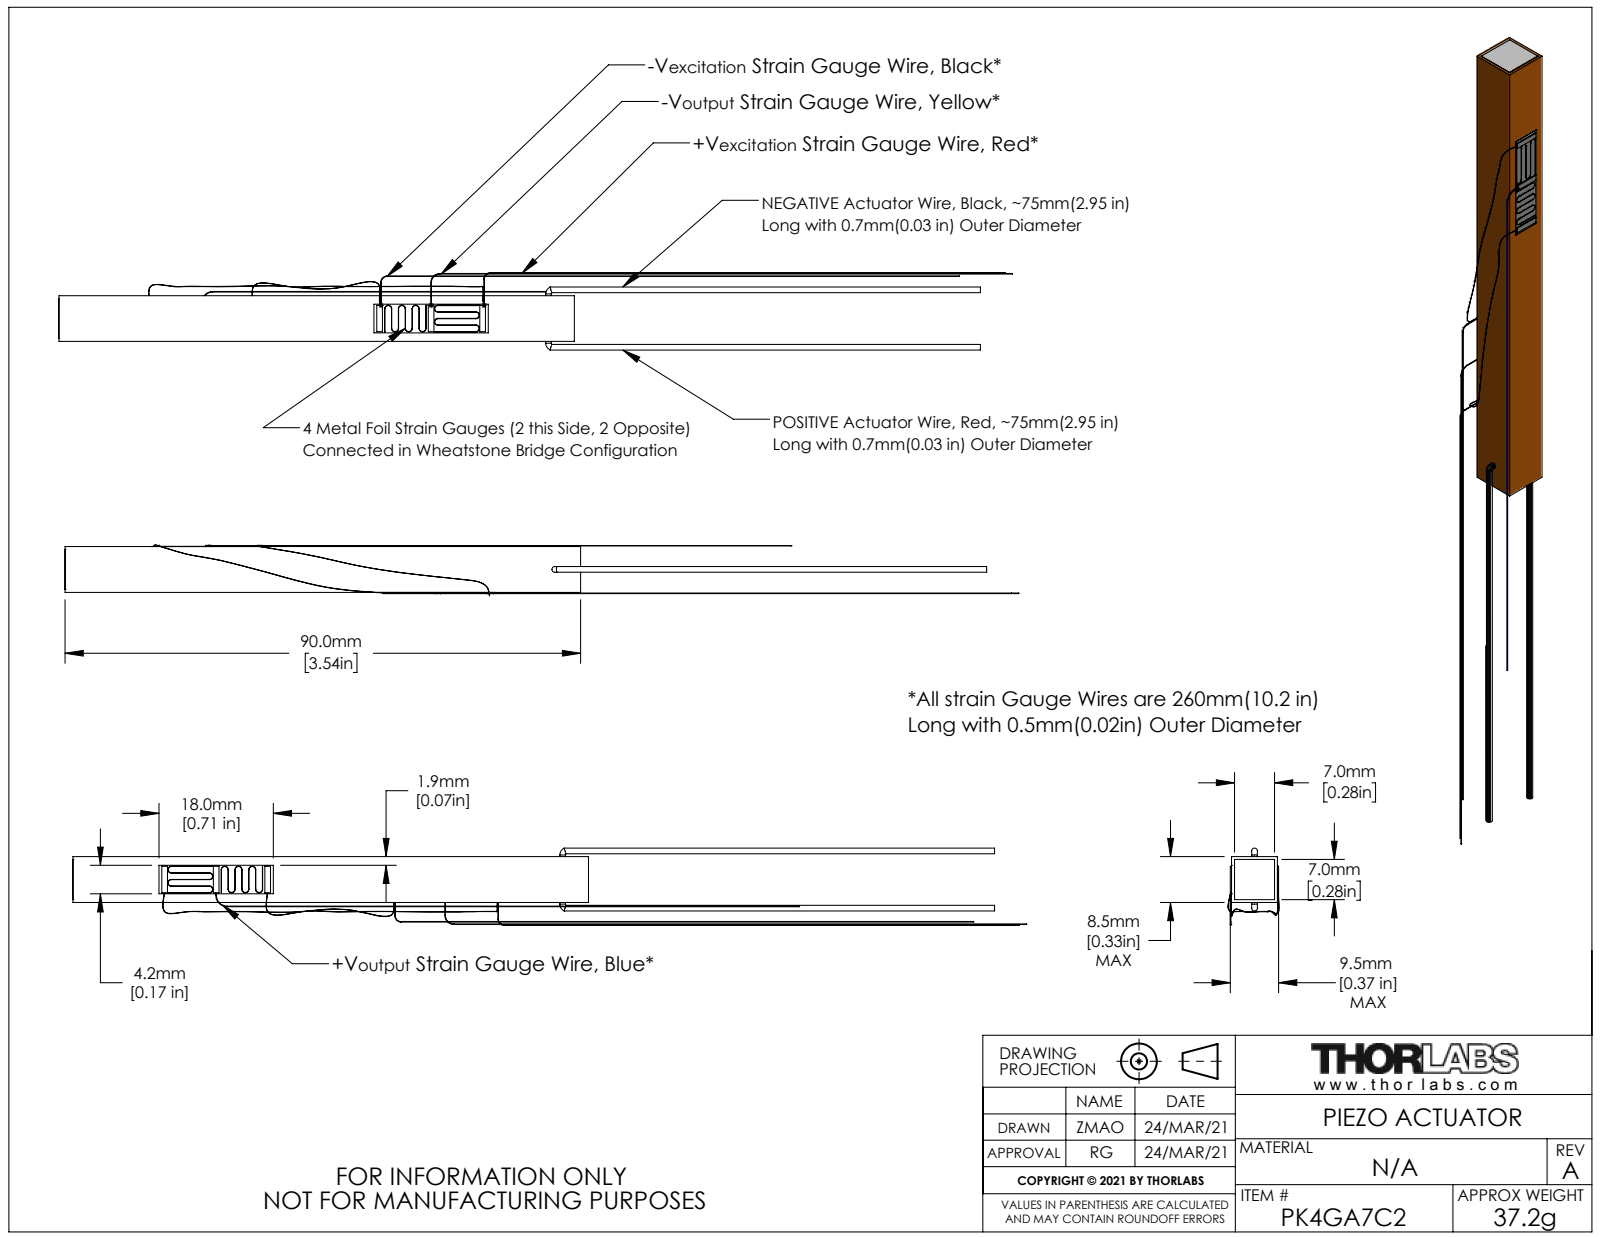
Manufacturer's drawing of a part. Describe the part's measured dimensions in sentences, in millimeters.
The part is named "CTN016915-E0W". Its 3-D file was written by "SolidWorks 2018 (AUTOMOTIVE_DESIGN)". It is 2 solids with 180 faces: 72 planar, 60 cylindrical and 48 other. Overall it measures 166.53 by 13.49 by 8.92 millimeters. Its volume is 5 891 cubic millimeters and its surface area 3 647 square millimeters. Round bosses or shafts: 3 of diameter 1. The main face-to-face distances are 8, 8.01, 8.02, 90, 8.21, 8.22, 89.99, 90.01, 8.42, 9.
